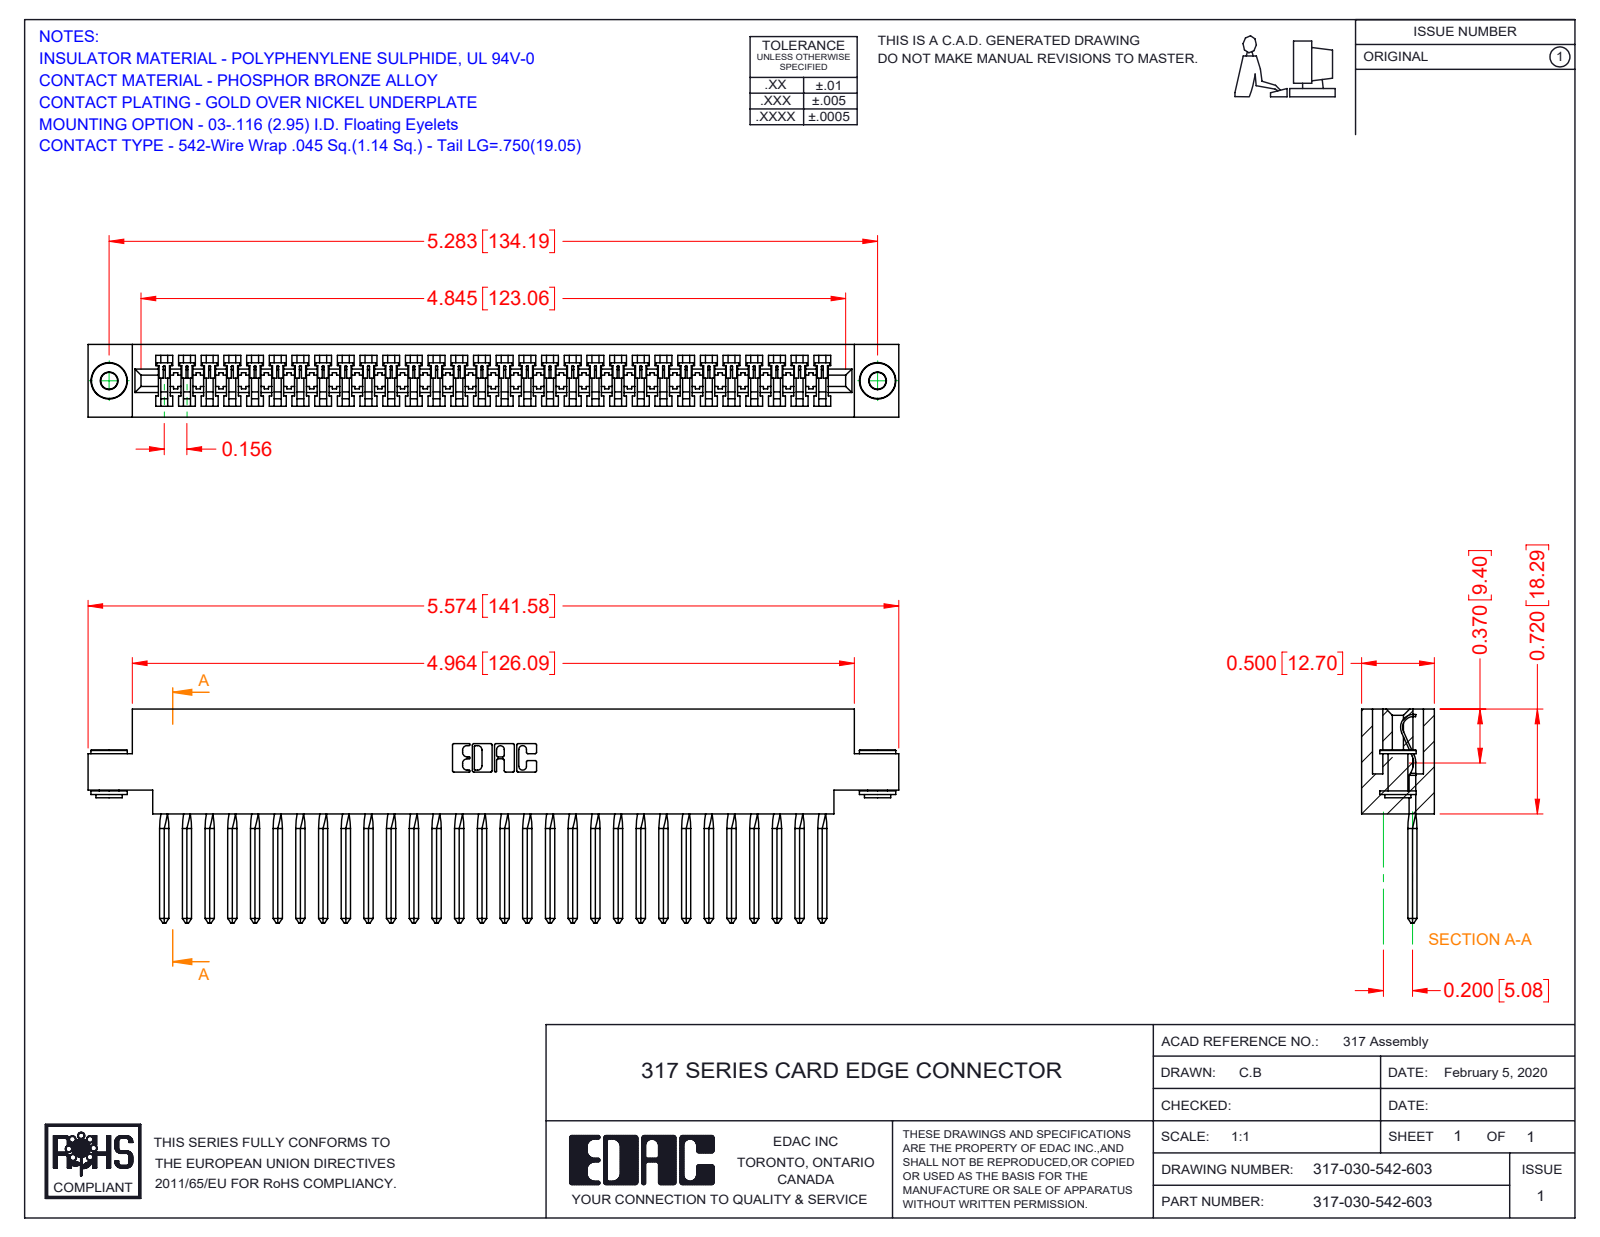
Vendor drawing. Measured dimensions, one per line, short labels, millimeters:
name: 317-030-542-603; 317 Part_.156 Dia - TH; 345-250-002_345-250-002-102; 317-290-003_542
written by: SolidWorks 2016 (CONFIG_CONTROL_DESIGN)
unit: mm
bodies: 33 solids, 2390 faces (1988 planar, 274 cylindrical, 128 other)
size: 141.6 × 37.3 × 12.7
volume: 21 570 mm³; area: 26 260 mm²
holes: 2× ⌀2.9, 2× ⌀4
bosses: 2× ⌀6.4, 2× ⌀4.6, 2× ⌀3.5
rounds: 60× R0.2, 22× R0.3, 6× R0.2, 6× R0.8, 3× R0.7, 1× R1.9, 1× R2.3, 1× R2.5
face distances: 12.7, 1.9, 10.8, 8.9, 2.8, 18.3, 3.5, 5.4, 7.3, 5.4
hole spacings: 134.2
